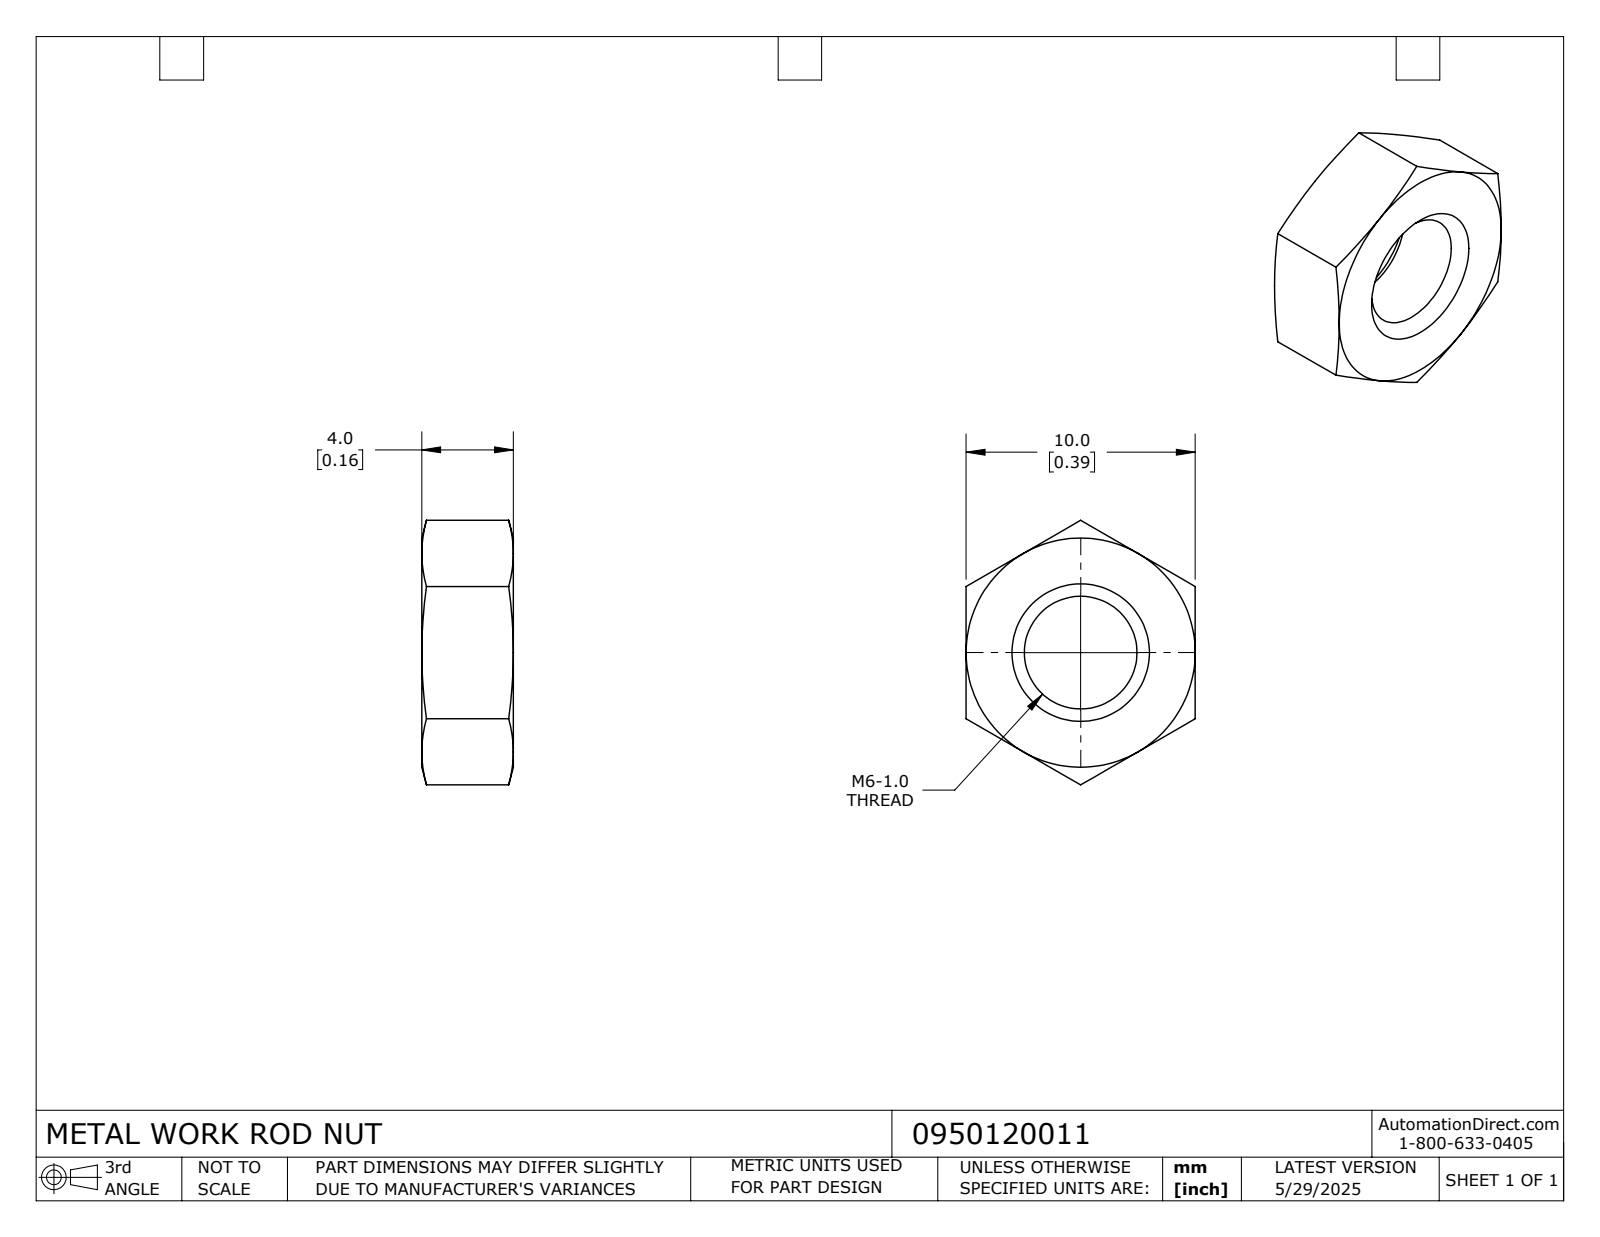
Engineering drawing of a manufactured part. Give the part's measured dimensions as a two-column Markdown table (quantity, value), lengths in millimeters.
| quantity | value |
| --- | --- |
| part name | 0950120011 |
| STEP written by | SolidWorks 2024 (CONFIG_CONTROL_DESIGN) |
| units | millimeters |
| bodies | 1 solid, 26 faces (8 planar, 2 cylindrical, 16 other) |
| overall size | 11.55 × 10 × 4 |
| volume | 265 mm³ |
| surface area | 322 mm² |
| round holes (diameter × count) | 4.92 × 1 |
| main face-to-face distances | 10, 4 |
